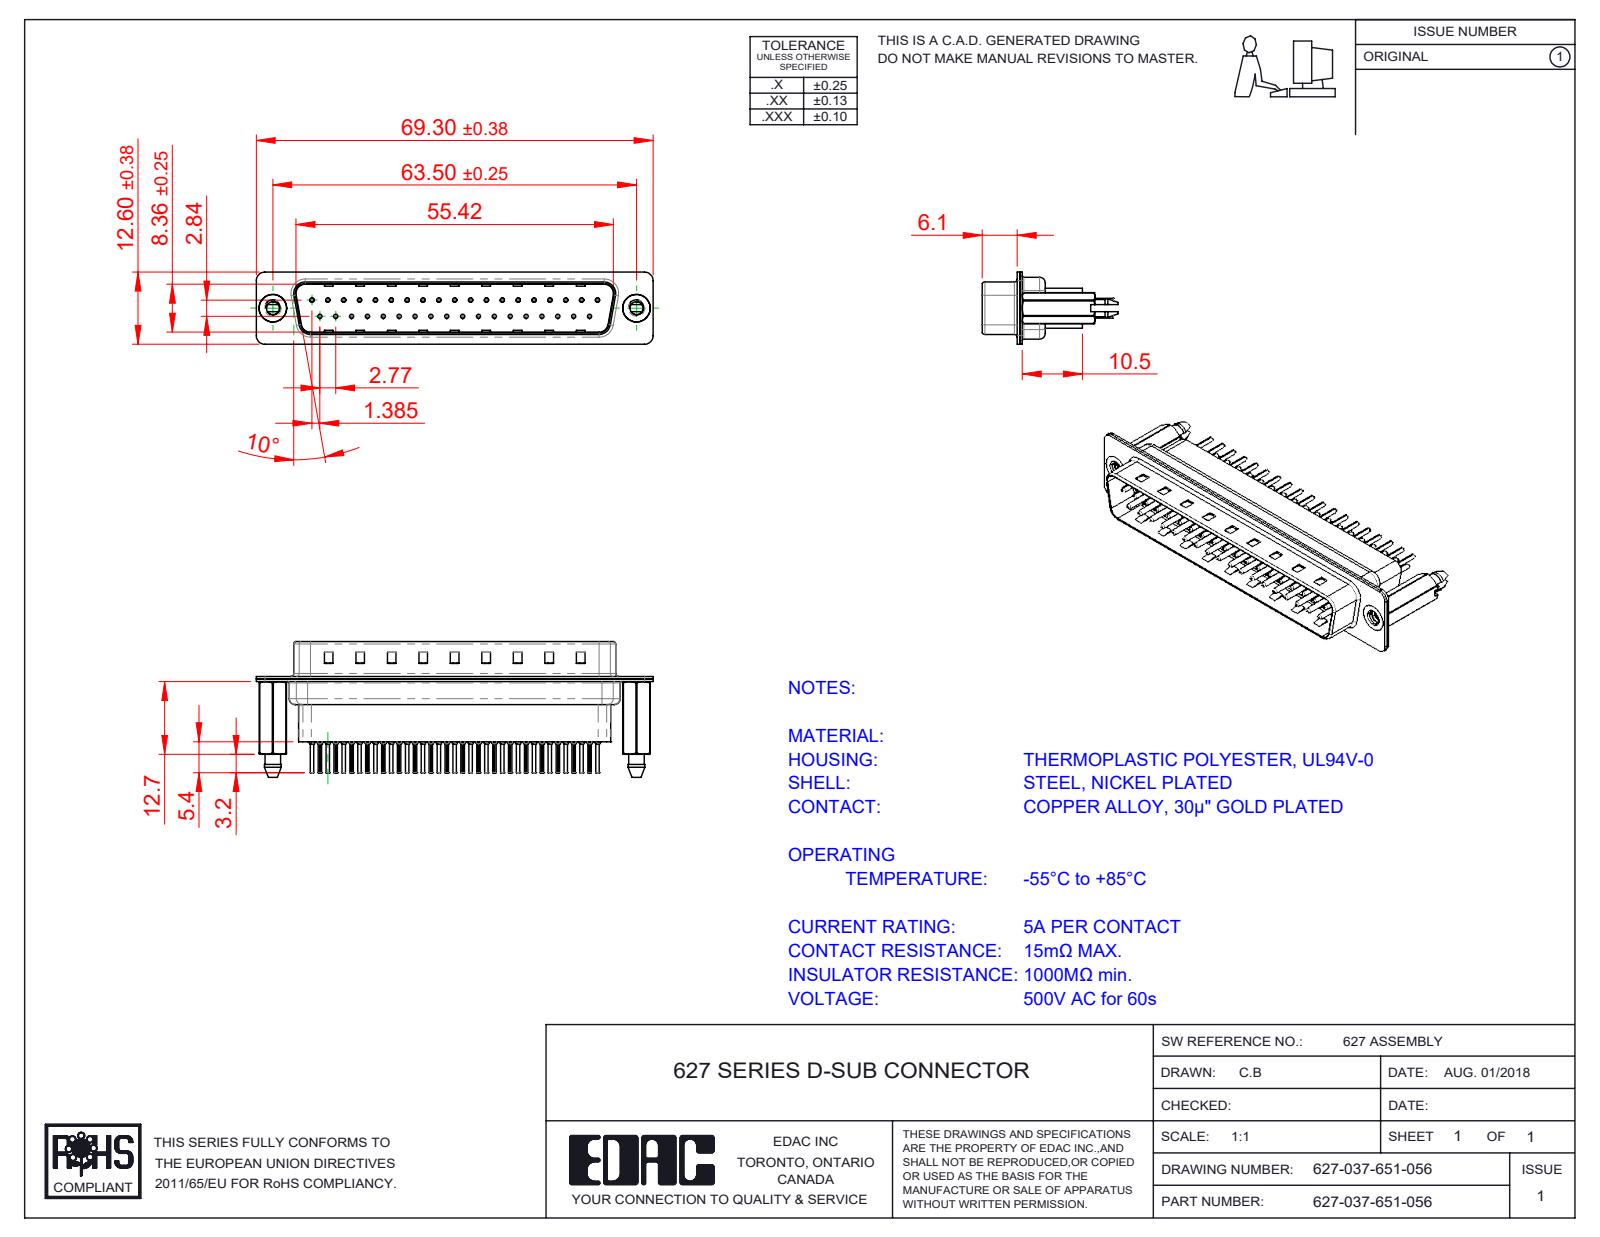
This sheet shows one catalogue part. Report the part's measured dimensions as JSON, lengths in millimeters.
{"part_name": "627 Shell Front_37 Contacts; 627 Contact Row 1_41; 627 Housing_37 HP; 627-037-651-056 (+3 more)", "step_written_by": "SolidWorks 2020 (CONFIG_CONTROL_DESIGN)", "units": "millimeters", "bodies": {"solids": 42, "faces": 4146, "planar": 1123, "cylindrical": 1576, "other": 1447}, "overall_size": [69.3, 23.6, 12.6], "volume_mm3": 5636, "surface_area_mm2": 14445, "round_holes": [[0.2, 37], [0.35, 37], [1.1, 37], [1.6, 37], [2.26, 2], [4, 2], [4.8, 2]], "round_bosses_or_shafts": [[2, 37], [1.5, 37], [0.75, 37], [0.6, 37], [4.9, 2]], "partial_cylinders_radius": [[0.1, 74], [1.5, 18], [2, 12], [1.6, 10], [0.5, 8], [0.25, 4], [0.6, 4], [0.65, 4]], "face_to_face_distances": [0.4, 0.82, 9.58, 0.68, 7.68, 0.45, 1.5, 1.08, 8.08, 8.76], "hole_center_spacings": [3.16, 2.77, 5.54, 8.31, 5.04, 10.1, 11.08, 12.78]}
